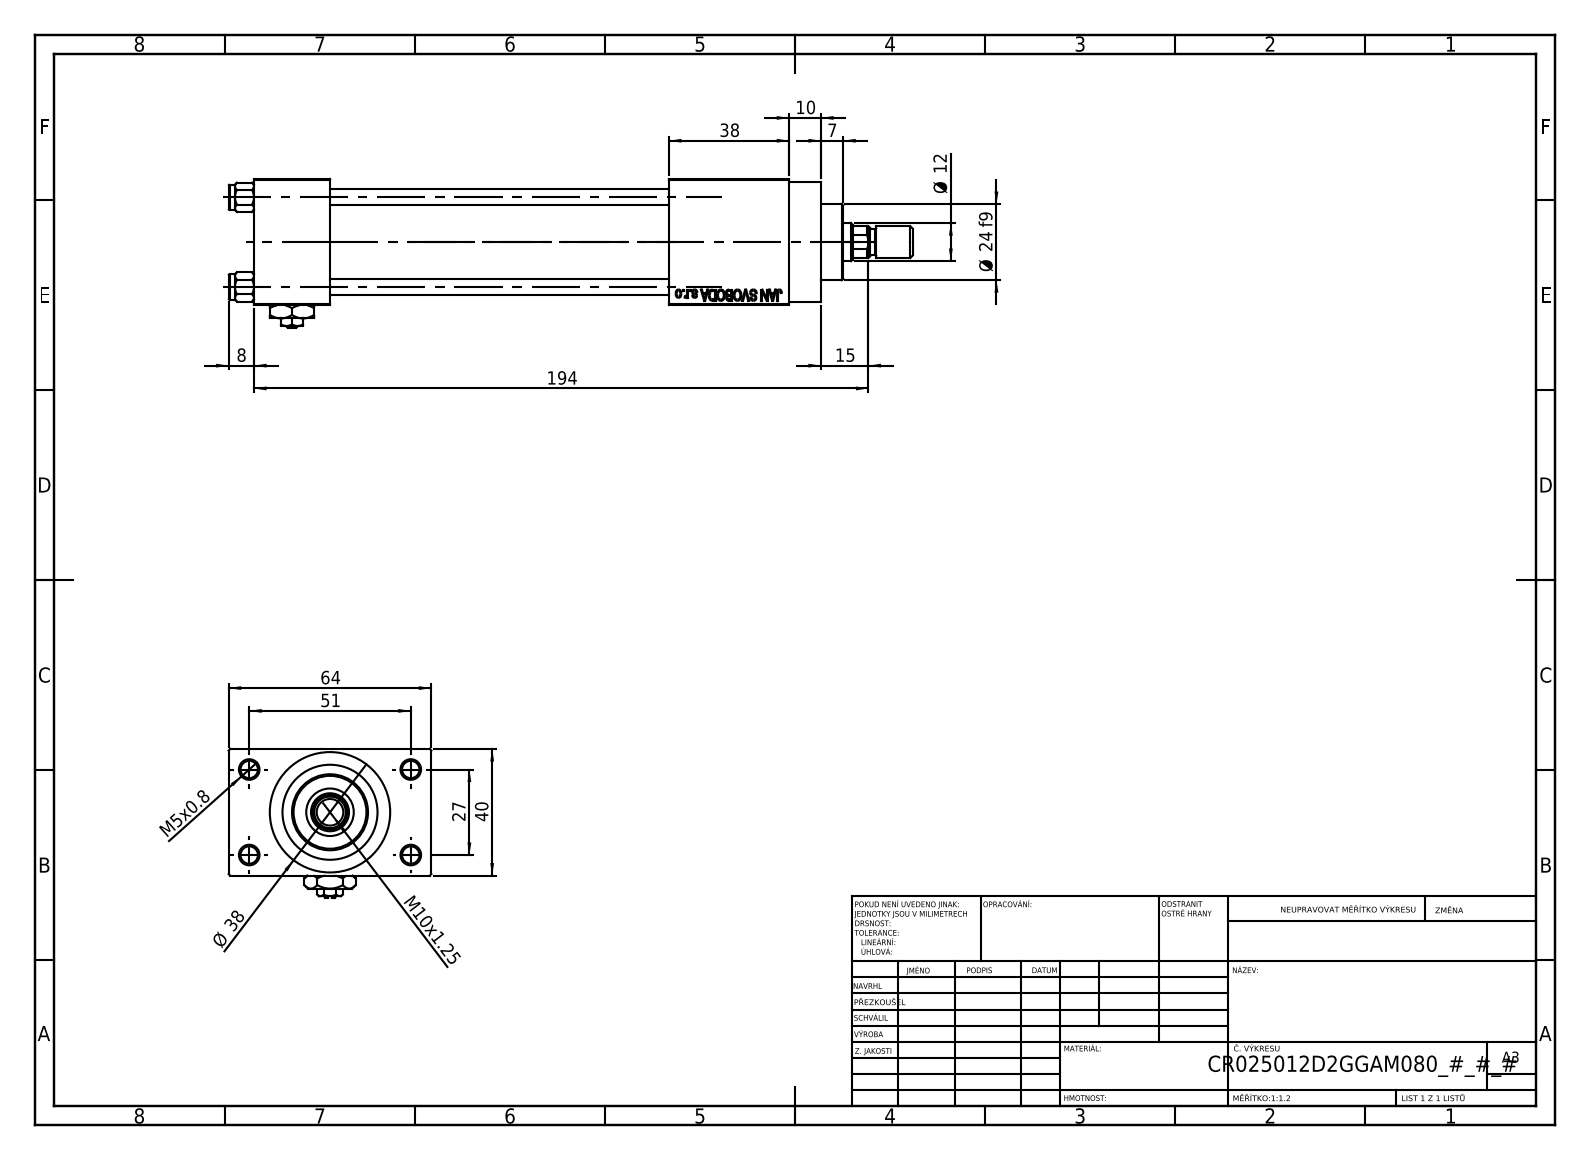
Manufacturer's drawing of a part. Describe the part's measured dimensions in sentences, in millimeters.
The part is named "ROD_END_AH; V215CR_D_Body; V215_VC_A; V215CR_D_TYCINKA (+3 more)". Its 3-D file was written by "SolidWorks 2019 (CONFIG_CONTROL_DESIGN)". It is 13 solids with 1169 faces: 523 planar, 100 cylindrical and 546 other. Overall it measures 216 by 64 by 47 millimeters. Its volume is 202 523 cubic millimeters and its surface area 79 951 square millimeters. Round holes: 4 of diameter 5, 4 of diameter 5.5, 3 of diameter 20, 2 of diameter 7, 2 of diameter 13.16, 1 of diameter 6.5, 1 of diameter 12, 1 of diameter 15, 1 of diameter 25, 1 of diameter 30. Round bosses or shafts: 5 of diameter 8, 1 of diameter 38, 1 of diameter 31, 1 of diameter 24, 1 of diameter 10. Partial cylindrical surfaces (rounded edges, fillets, slot ends): 1 of radius 5.5. The main face-to-face distances are 40, 12, 52, 107, 24, 131, 64, 38, 169, 145. The hole center spacings are 11.37, 20.01, 28.3, 28.85, 29.89, 39.66, 48.34, 27.
